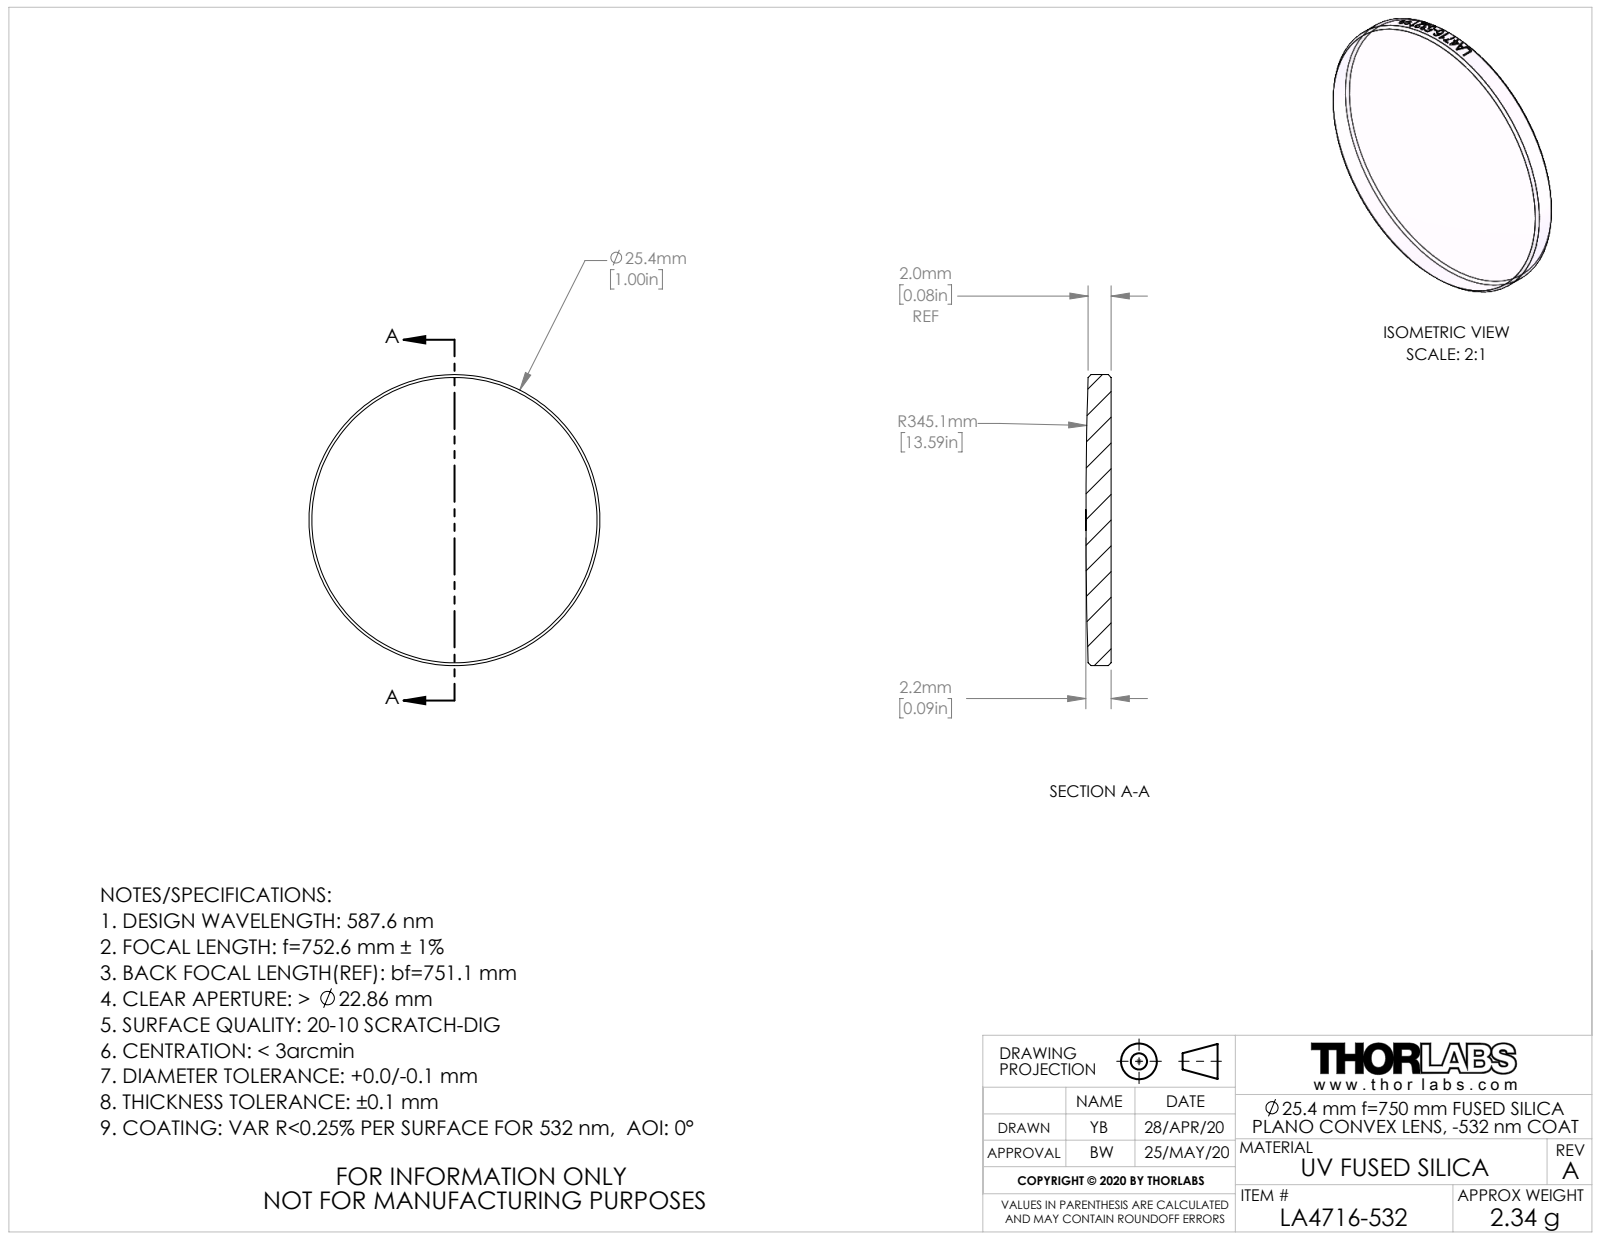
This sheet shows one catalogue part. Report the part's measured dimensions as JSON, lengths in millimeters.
{"part_name": "CTN015738-E0W", "step_written_by": "SolidWorks 2018 (AUTOMOTIVE_DESIGN)", "units": "millimeters", "bodies": {"solids": 1, "faces": 26, "planar": 1, "cylindrical": 19, "other": 6}, "overall_size": [25.4, 25.4, 2.2], "volume_mm3": 1062, "surface_area_mm2": 1150, "round_bosses_or_shafts": [[25.4, 1]]}
